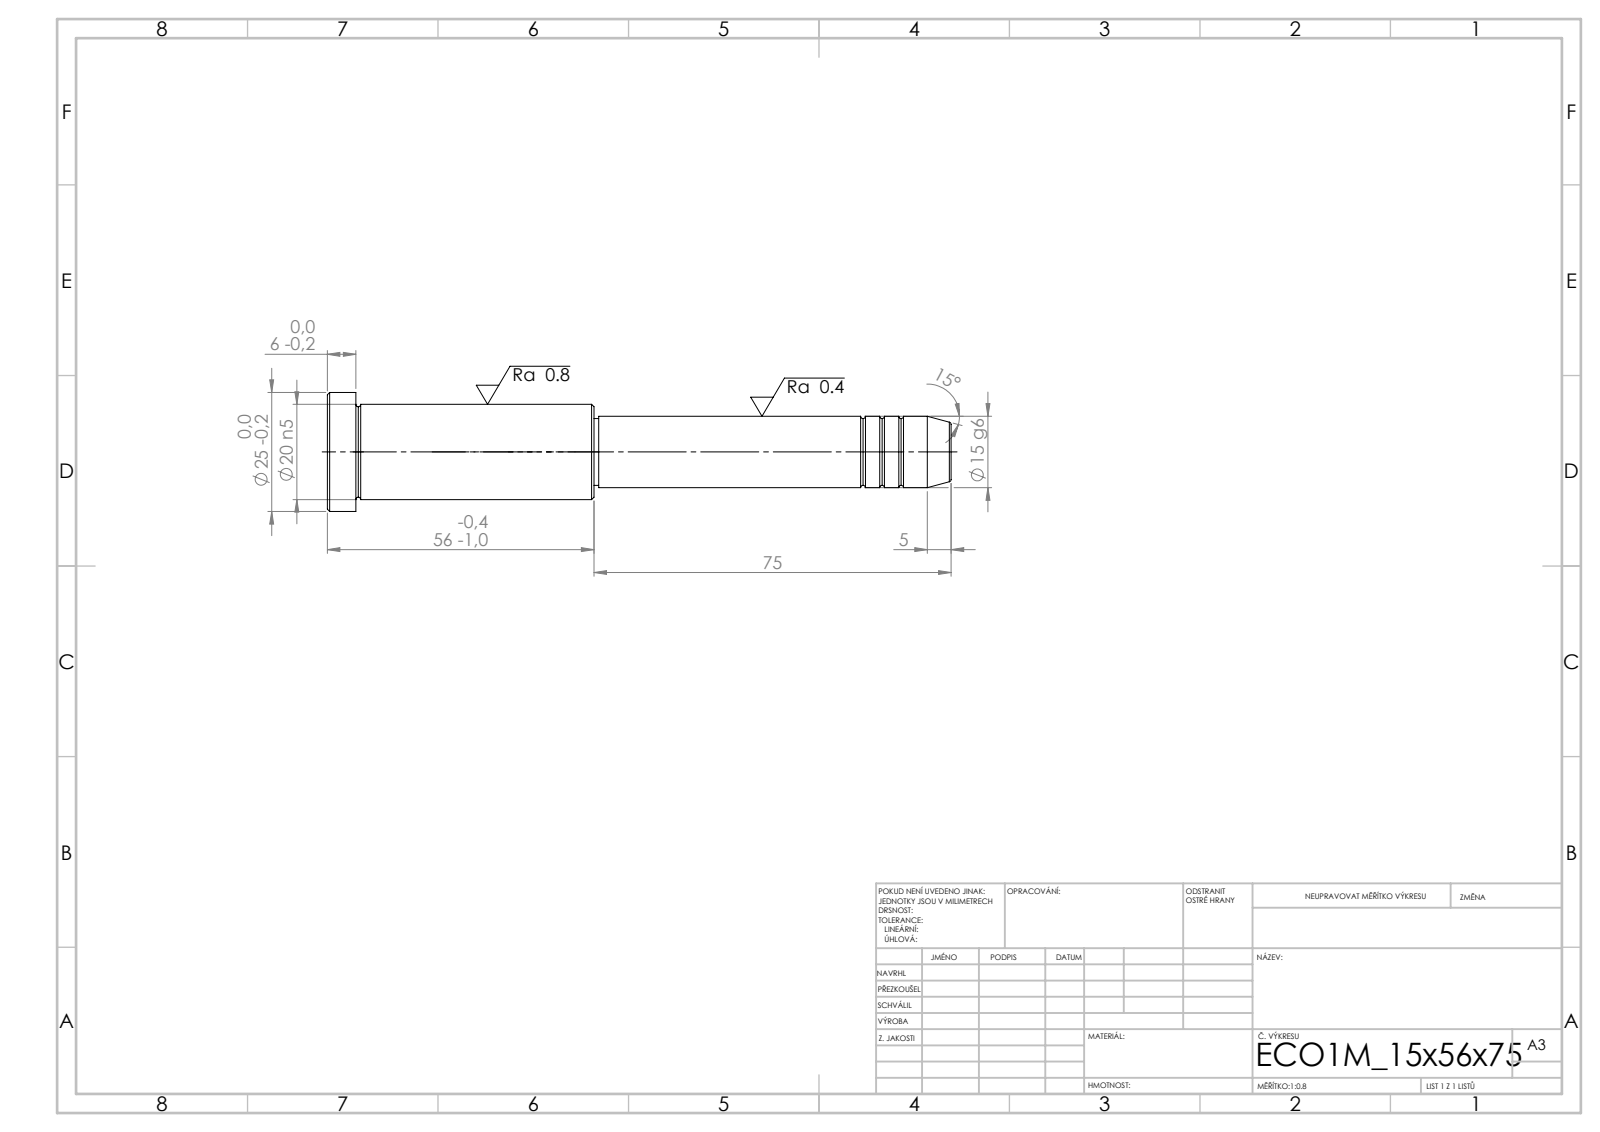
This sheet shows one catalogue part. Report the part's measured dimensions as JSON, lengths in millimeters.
{"step_written_by": "SolidWorks 2019 (CONFIG_CONTROL_DESIGN)", "units": "millimeters", "bodies": {"solids": 1, "faces": 43, "planar": 5, "cylindrical": 14, "other": 24}, "overall_size": [131, 25, 25], "volume_mm3": 31639, "surface_area_mm2": 8158, "round_bosses_or_shafts": [[25, 1], [20, 1], [15, 1], [14, 1]], "face_to_face_distances": [6, 50, 56, 75, 125, 131, 74, 1, 51, 57]}
